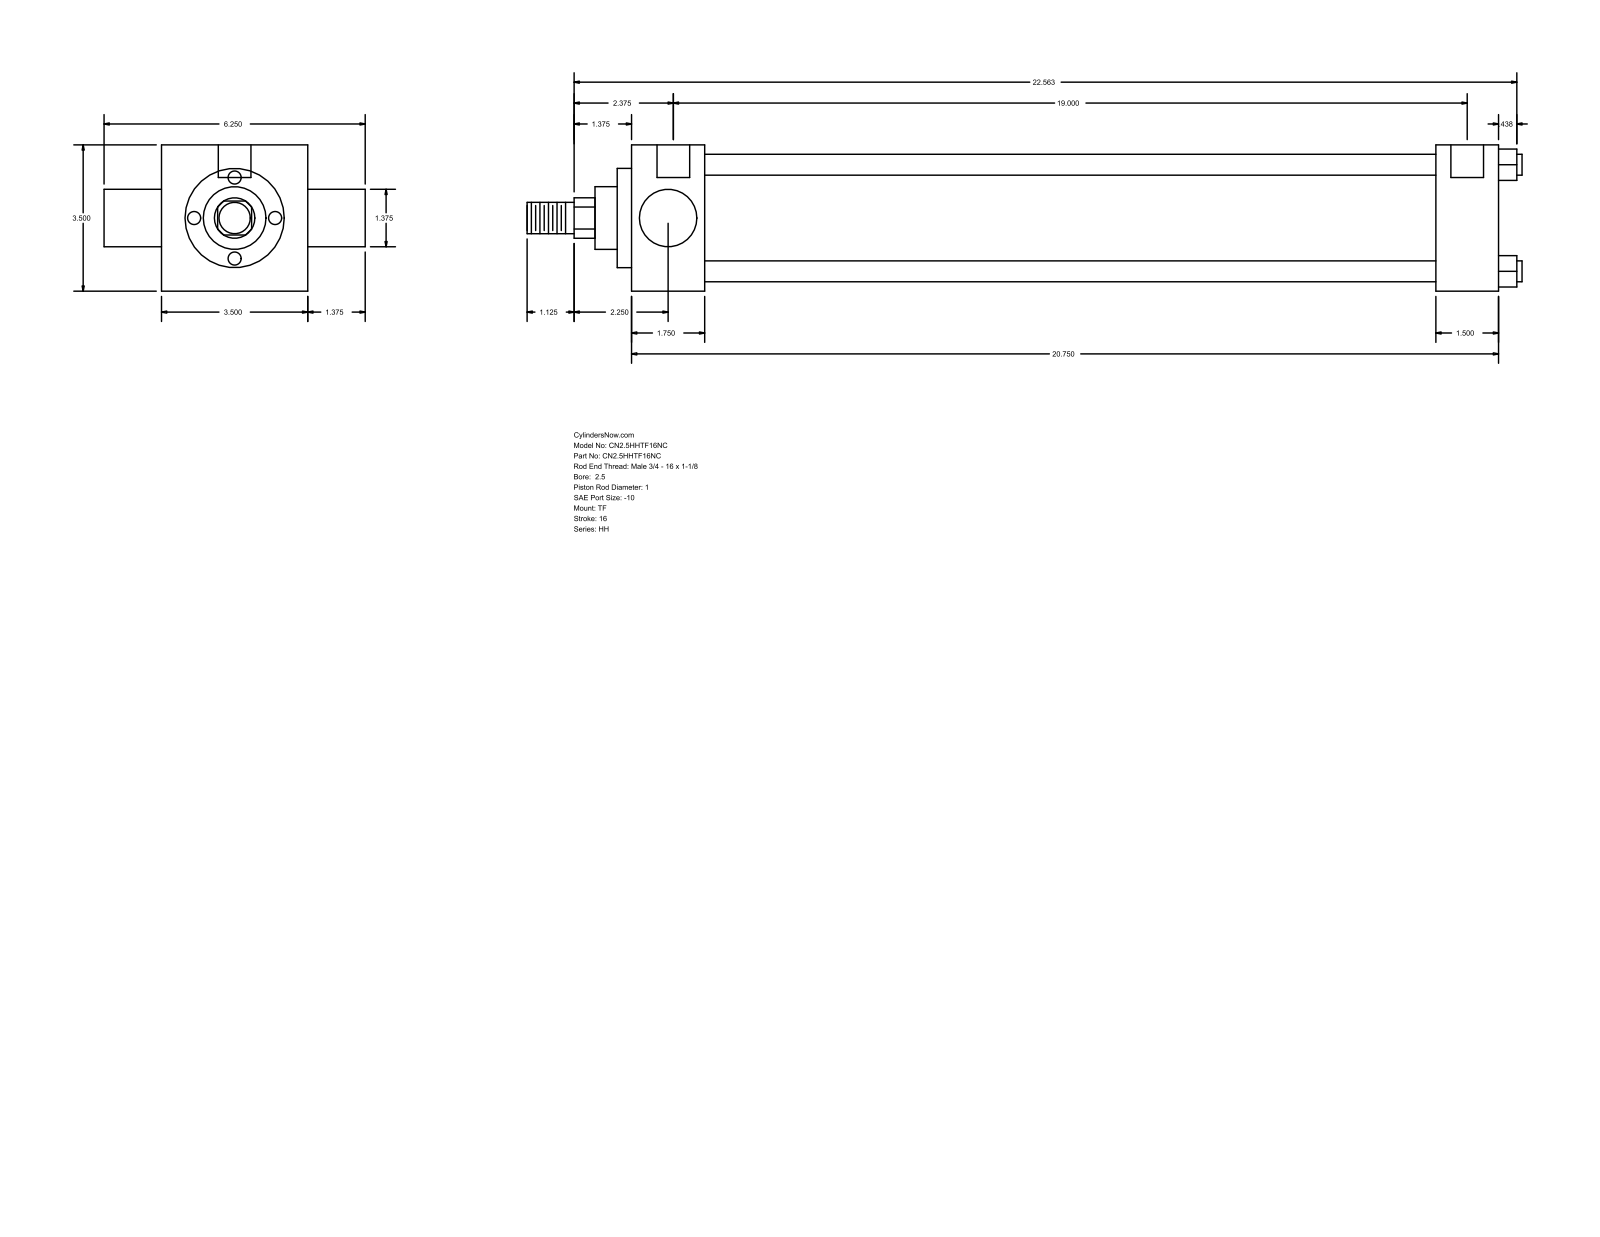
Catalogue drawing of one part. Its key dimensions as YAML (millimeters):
part_name: "HH_TF__0250_1"
step_written_by: "GSSL Pune (CONFIG_CONTROL_DESIGN)"
units: millimeters
bodies: {solids: 0, faces: 86, planar: 61, cylindrical: 25, other: 0}
overall_size: [604.84, 158.75, 88.9]
round_holes:
  - {diameter: 5.56, count: 3}
  - {diameter: 19.84, count: 2}
round_bosses_or_shafts:
  - {diameter: 12.7, count: 4}
  - {diameter: 73.03, count: 1}
  - {diameter: 60.33, count: 1}
  - {diameter: 38.1, count: 1}
  - {diameter: 34.92, count: 1}
  - {diameter: 25.4, count: 1}
  - {diameter: 19.05, count: 1}
partial_cylinders:
  - {radius: 12.29, count: 1}
face_to_face_distances: [88.9, 527.06, 38.1, 44.46, 482.6, 488.96, 444.5, 34.93, 123.83, 8.73]
hole_center_spacings: [1.59, 484.18, 482.59, 485.77]
